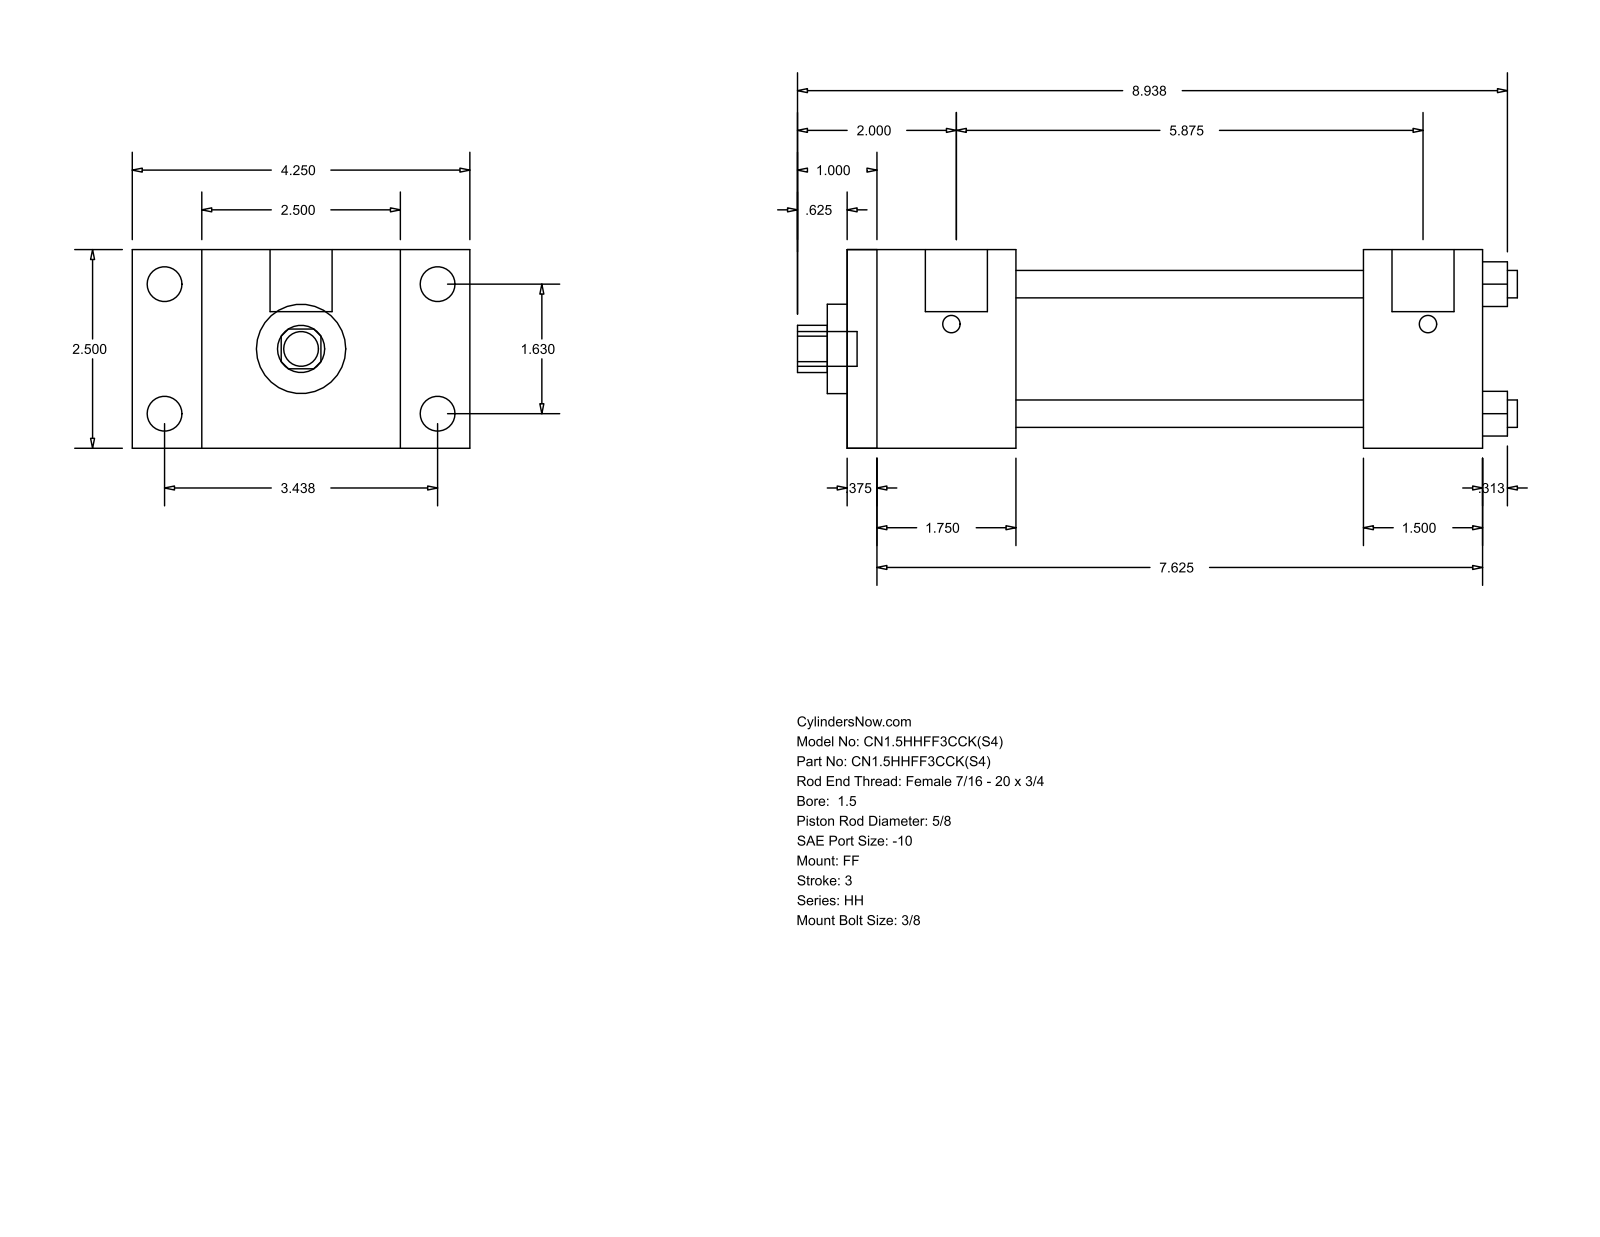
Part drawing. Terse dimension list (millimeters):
name: HH_FF__0150_0.625
written by: GSSL Pune (CONFIG_CONTROL_DESIGN)
unit: mm
bodies: 0 solids, 92 faces (64 planar, 28 cylindrical, 0 other)
size: 230.19 × 107.95 × 63.5
holes: 4× ⌀8.76, 1× ⌀15.88, 1× ⌀28.57, 1× ⌀44.45
bosses: 4× ⌀11.13, 4× ⌀5.56, 2× ⌀19.84, 1× ⌀11.11
rounds: 1× R7.54
face distances: 63.5, 203.19, 9.52, 38.1, 193.67, 53.97, 44.45, 149.22, 165.09, 155.57
hole spacings: 29.27, 41.4, 58.55
